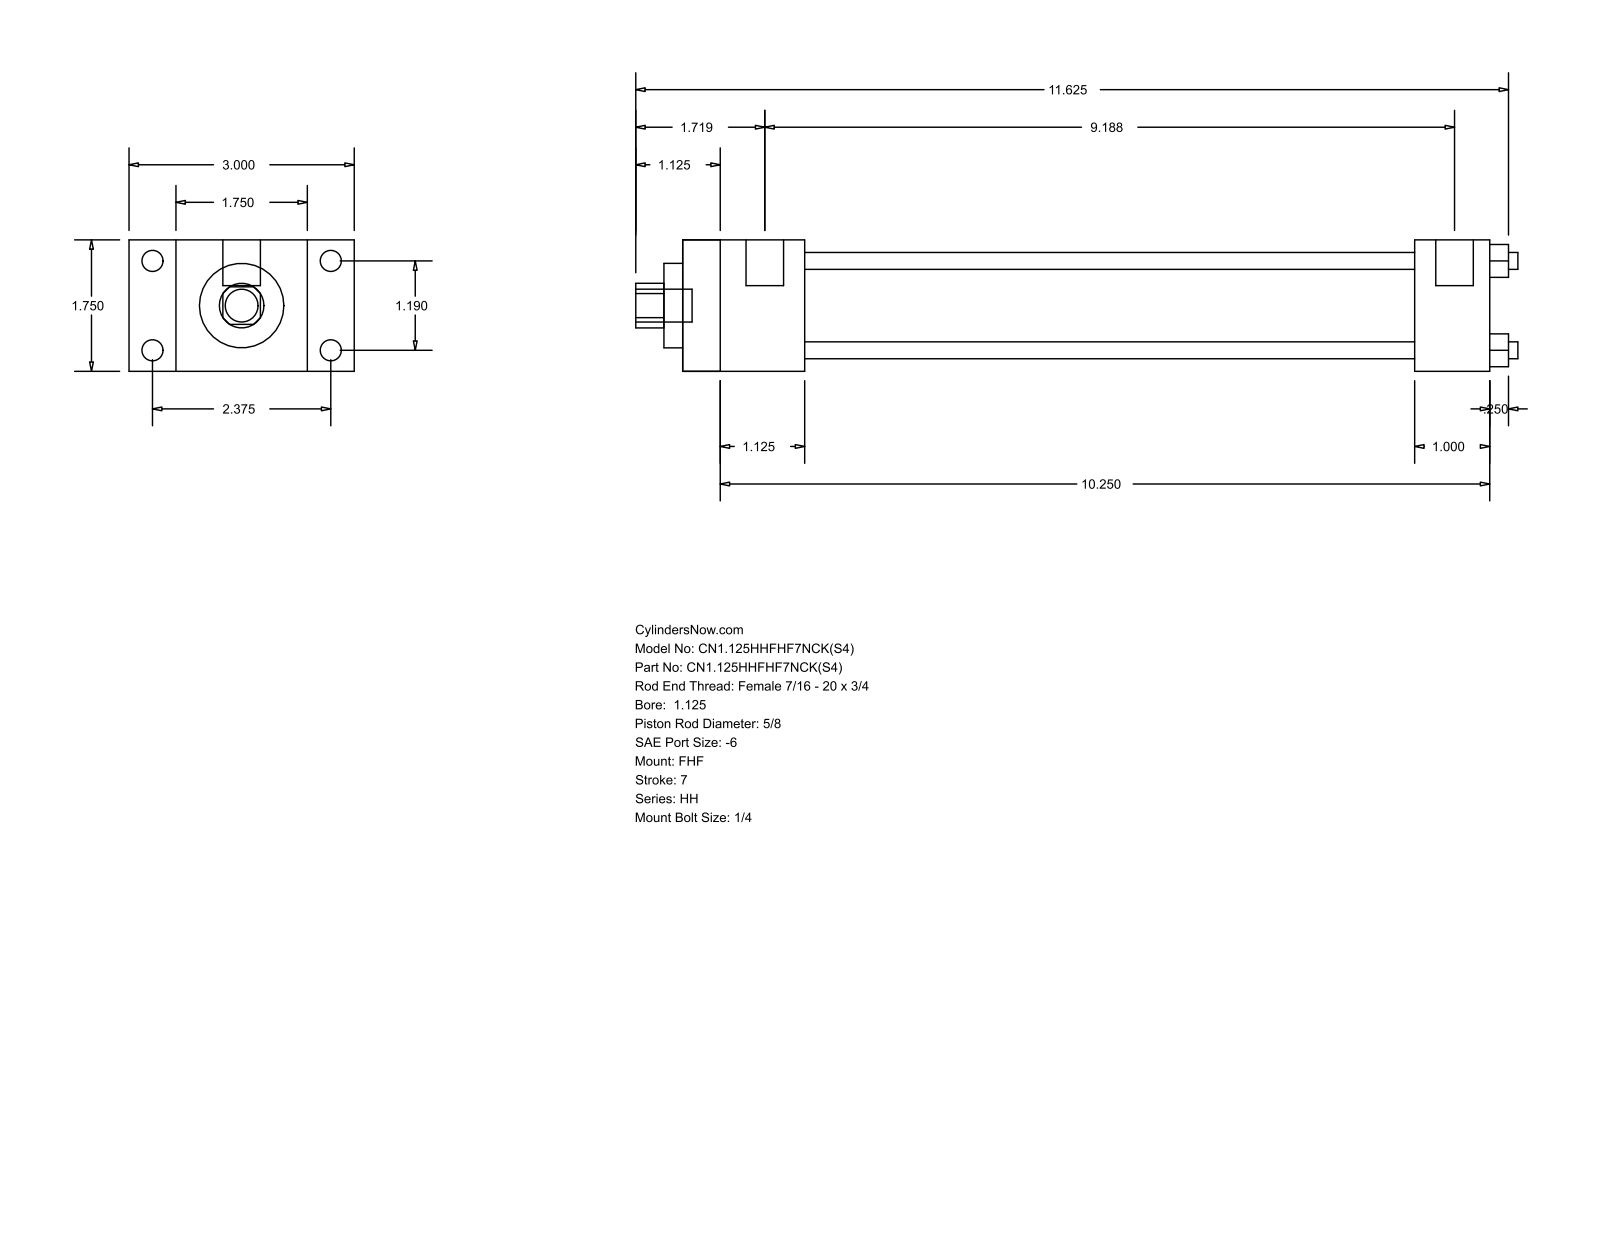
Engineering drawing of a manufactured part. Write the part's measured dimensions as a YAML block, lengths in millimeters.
part_name: "HH_FHF__0112_0.625"
step_written_by: "GSSL Pune (CONFIG_CONTROL_DESIGN)"
units: millimeters
bodies: {solids: 0, faces: 88, planar: 60, cylindrical: 28, other: 0}
overall_size: [298.45, 76.2, 44.45]
round_holes:
  - {diameter: 5.71, count: 4}
  - {diameter: 15.88, count: 1}
  - {diameter: 28.57, count: 1}
  - {diameter: 34.92, count: 1}
round_bosses_or_shafts:
  - {diameter: 7.14, count: 4}
  - {diameter: 5.56, count: 4}
  - {diameter: 12.7, count: 2}
  - {diameter: 11.11, count: 1}
partial_cylinders:
  - {radius: 7.54, count: 1}
face_to_face_distances: [44.46, 15.87, 60.33, 41.27, 76.2, 273.05, 231.78, 247.64, 206.37, 25.41]
hole_center_spacings: [21.37, 30.22, 42.74]
